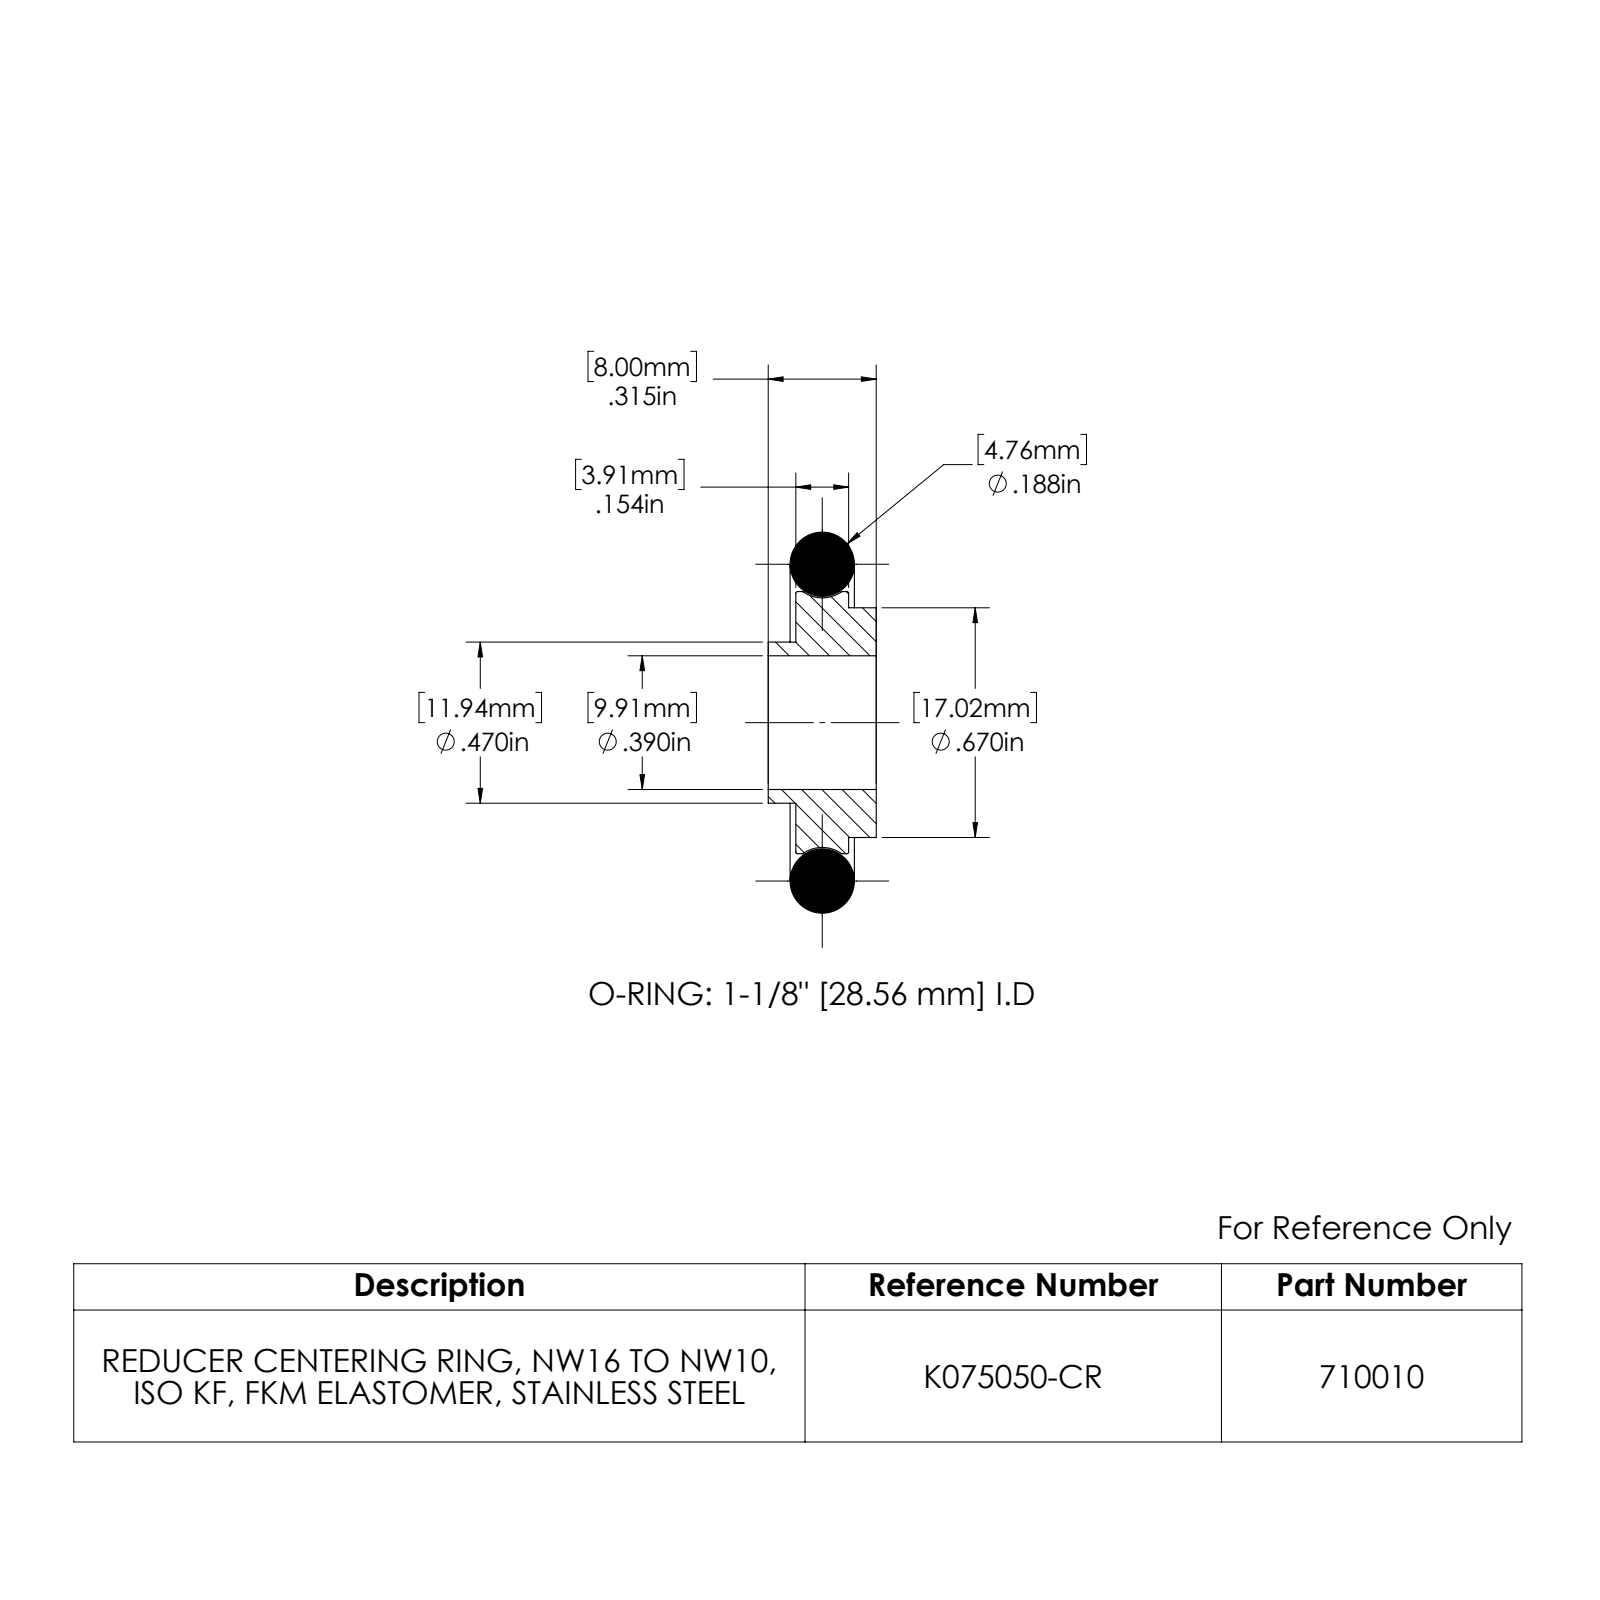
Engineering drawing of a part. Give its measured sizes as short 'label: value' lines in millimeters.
name: 710010
written by: SolidWorks 2022 (AUTOMOTIVE_DESIGN)
unit: mm
bodies: 2 solids, 30 faces (4 planar, 10 cylindrical, 16 other)
size: 28.2 × 28.2 × 8
volume: 2 490 mm³; area: 2 214 mm²
holes: 1× ⌀9.9
bosses: 1× ⌀19.4, 1× ⌀17, 1× ⌀11.9
face distances: 6, 2, 3.9, 8
